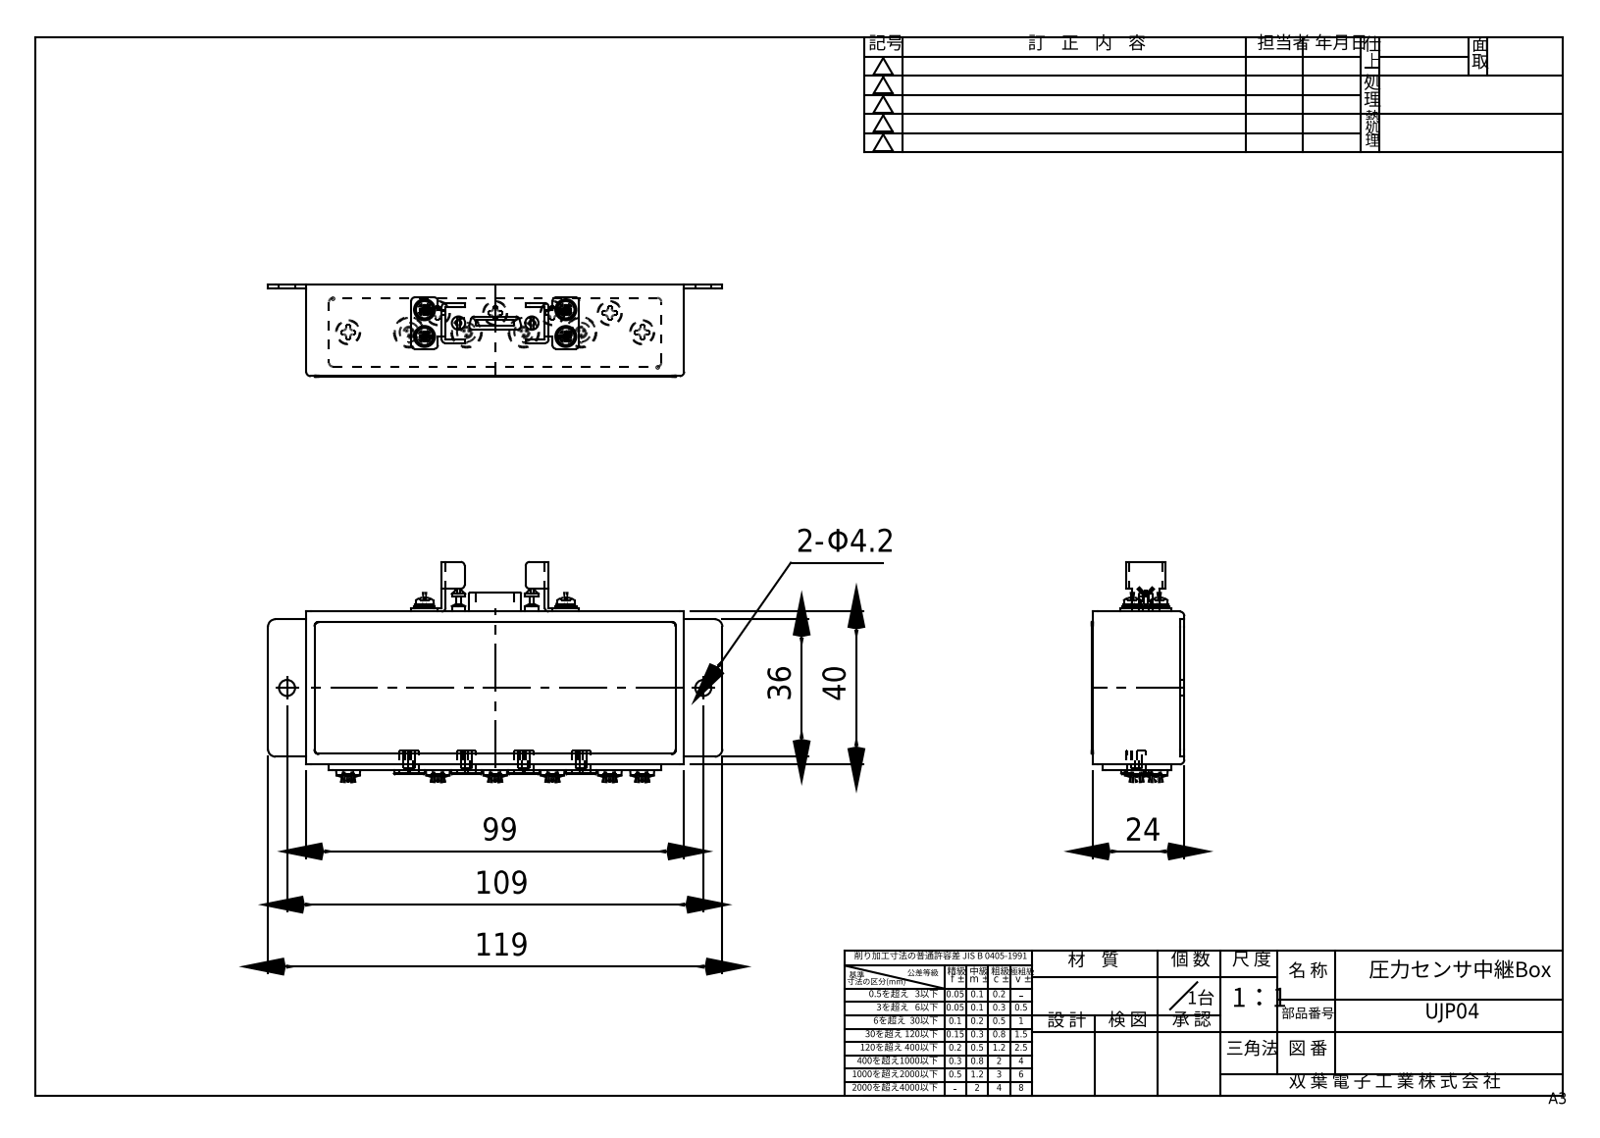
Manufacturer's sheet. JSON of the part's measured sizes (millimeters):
{"step_written_by": "XStep 1.0 (automotive_design)", "units": "millimeters", "bodies": {"solids": 1, "faces": 496, "planar": 314, "cylindrical": 142, "other": 40}, "overall_size": [119, 56.44, 24.2], "volume_mm3": 99809, "surface_area_mm2": 18774, "round_holes": [[0.6, 12], [2.47, 4], [5, 4], [4.2, 2]], "round_bosses_or_shafts": [[8, 4], [5.5, 4], [4.8, 4], [4.5, 4], [3, 4], [2.38, 4], [3.5, 2], [1.2, 2]], "partial_cylinders_radius": [[1, 26], [0.3, 24], [0.7, 24], [1.2, 4], [2.75, 4]], "face_to_face_distances": [24.2, 1, 41.6, 99, 1.6, 40, 23.2, 23, 24, 2.5], "hole_center_spacings": [0.8, 1.38, 15, 30, 14.32, 14.36, 15.02, 15.7]}
